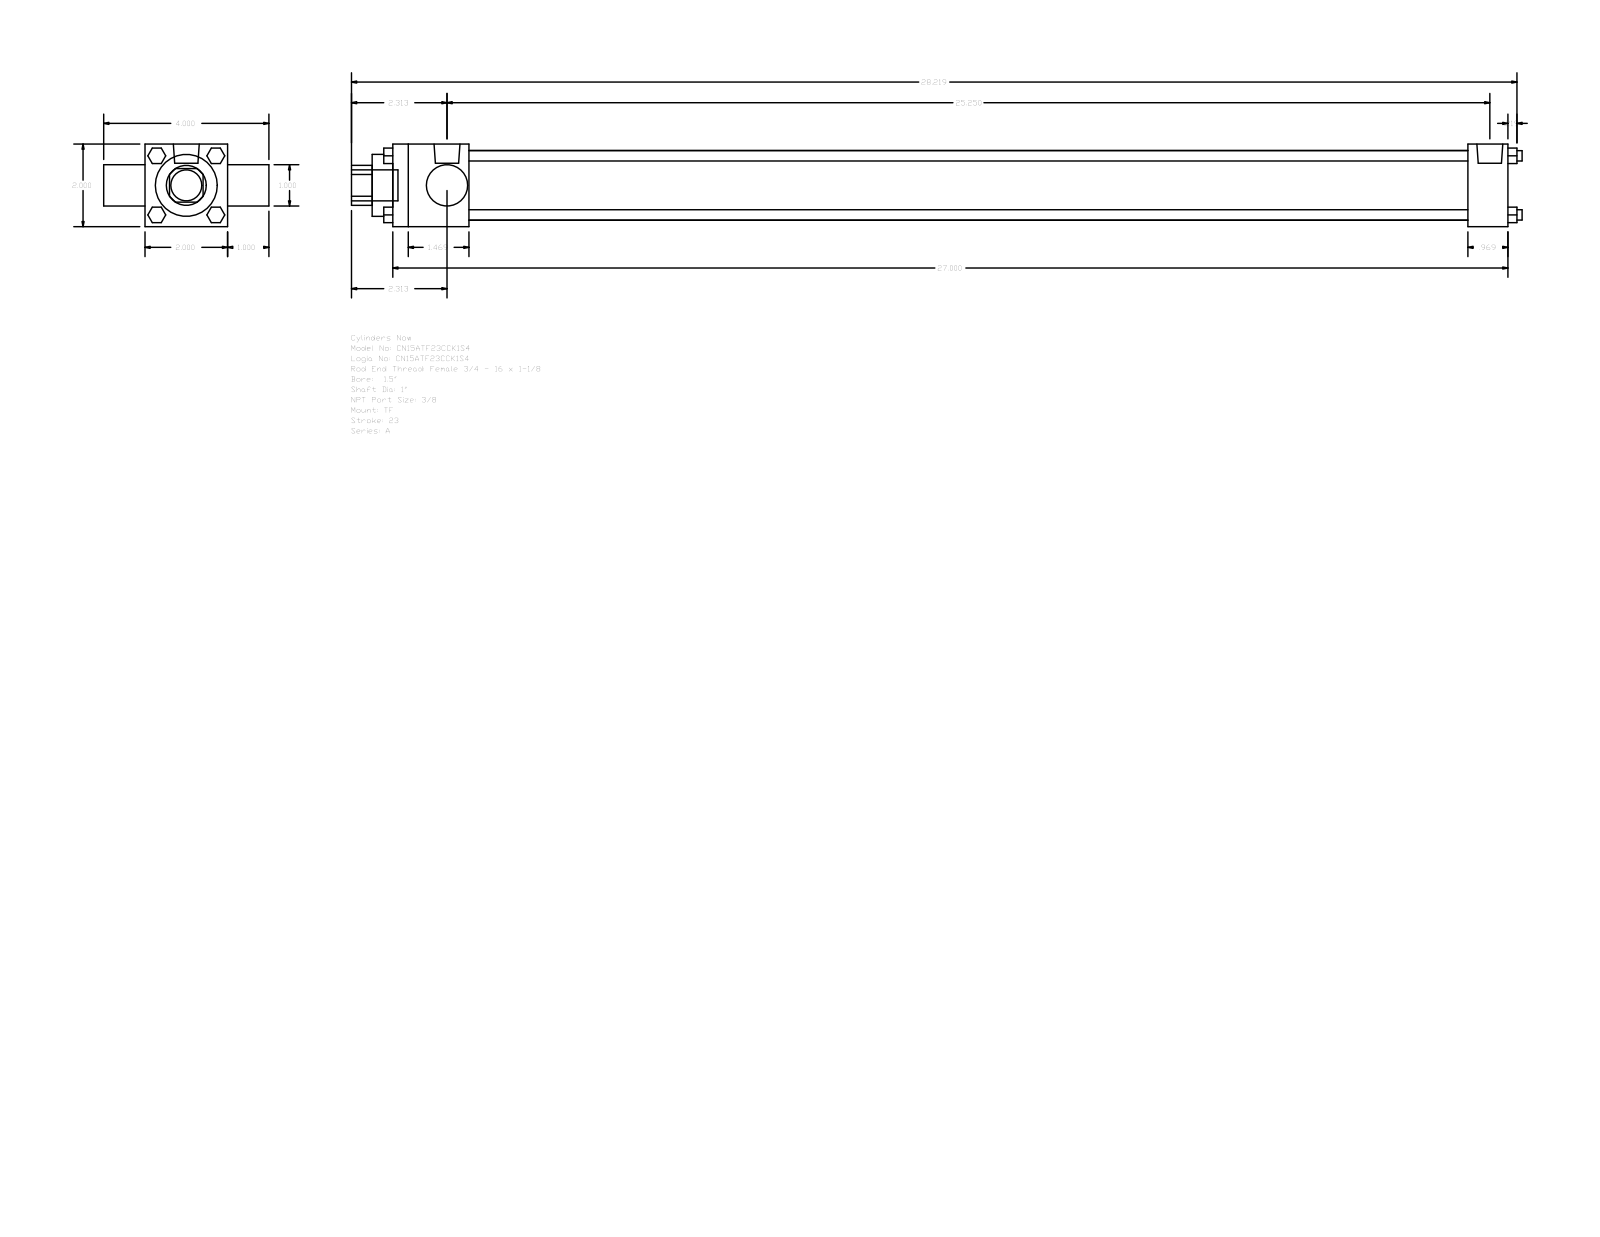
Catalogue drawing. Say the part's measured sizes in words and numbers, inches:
The part is named "A_TF__0150_1". Its 3-D file was written by "GSSL Pune (CONFIG_CONTROL_DESIGN)". It is 0 solids with 120 faces: 92 planar, 28 cylindrical and 0 other. Overall it measures 28.344 by 4 by 2 inches. Round holes: 2 of diameter 1, 1 of diameter 1.5, 1 of diameter 1.69. Round bosses or shafts: 4 of diameter 0.25, 3 of diameter 0.219, 2 of diameter 0.627, 1 of diameter 0.75. Partial cylindrical surfaces (rounded edges, fillets, slot ends): 1 of radius 0.484. The main face-to-face distances are 2, 1, 27, 3, 1.844, 26.031, 24.187, 25.156, 0.969, 0.5.
